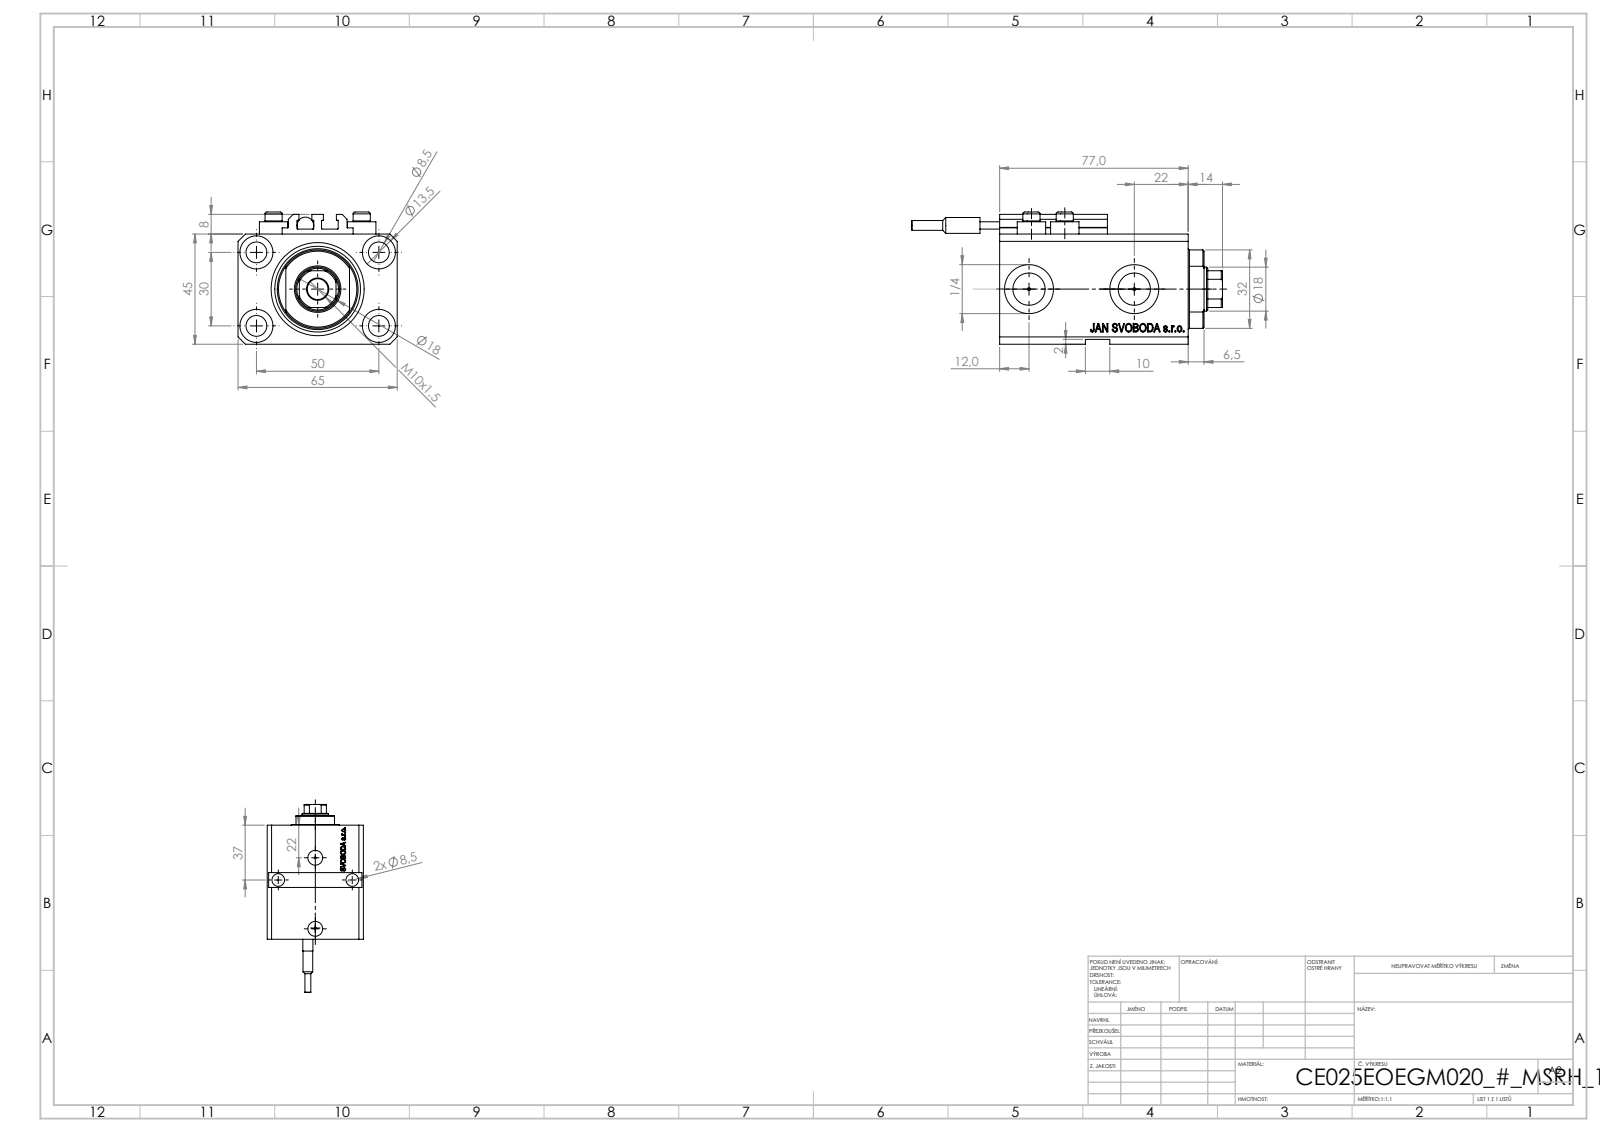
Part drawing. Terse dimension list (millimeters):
name: V250CE_C_VCP; ALLEN BOLT V250CE; V250CE_E_Body; V250CE_VC_E (+1 more)
written by: SolidWorks 2019 (CONFIG_CONTROL_DESIGN)
unit: mm
bodies: 9 solids, 1093 faces (527 planar, 132 cylindrical, 434 other)
size: 127 × 65 × 54
volume: 201 561 mm³; area: 60 560 mm²
holes: 7× ⌀8.5, 4× ⌀1.25, 4× ⌀4, 4× ⌀13.5, 2× ⌀10, 2× ⌀13.16, 2× ⌀20, 1× ⌀18, 1× ⌀25, 1× ⌀38
bosses: 4× ⌀11.6, 4× ⌀7, 1× ⌀6.8, 1× ⌀6.5, 1× ⌀4
rounds: 10× R0.2, 1× R8.5, 1× R16
face distances: 45, 65, 63, 14, 2, 77, 3, 47, 5, 6.9
hole spacings: 29.15, 50, 13.6, 15.12, 18.81, 18.97, 26.22, 26.61
